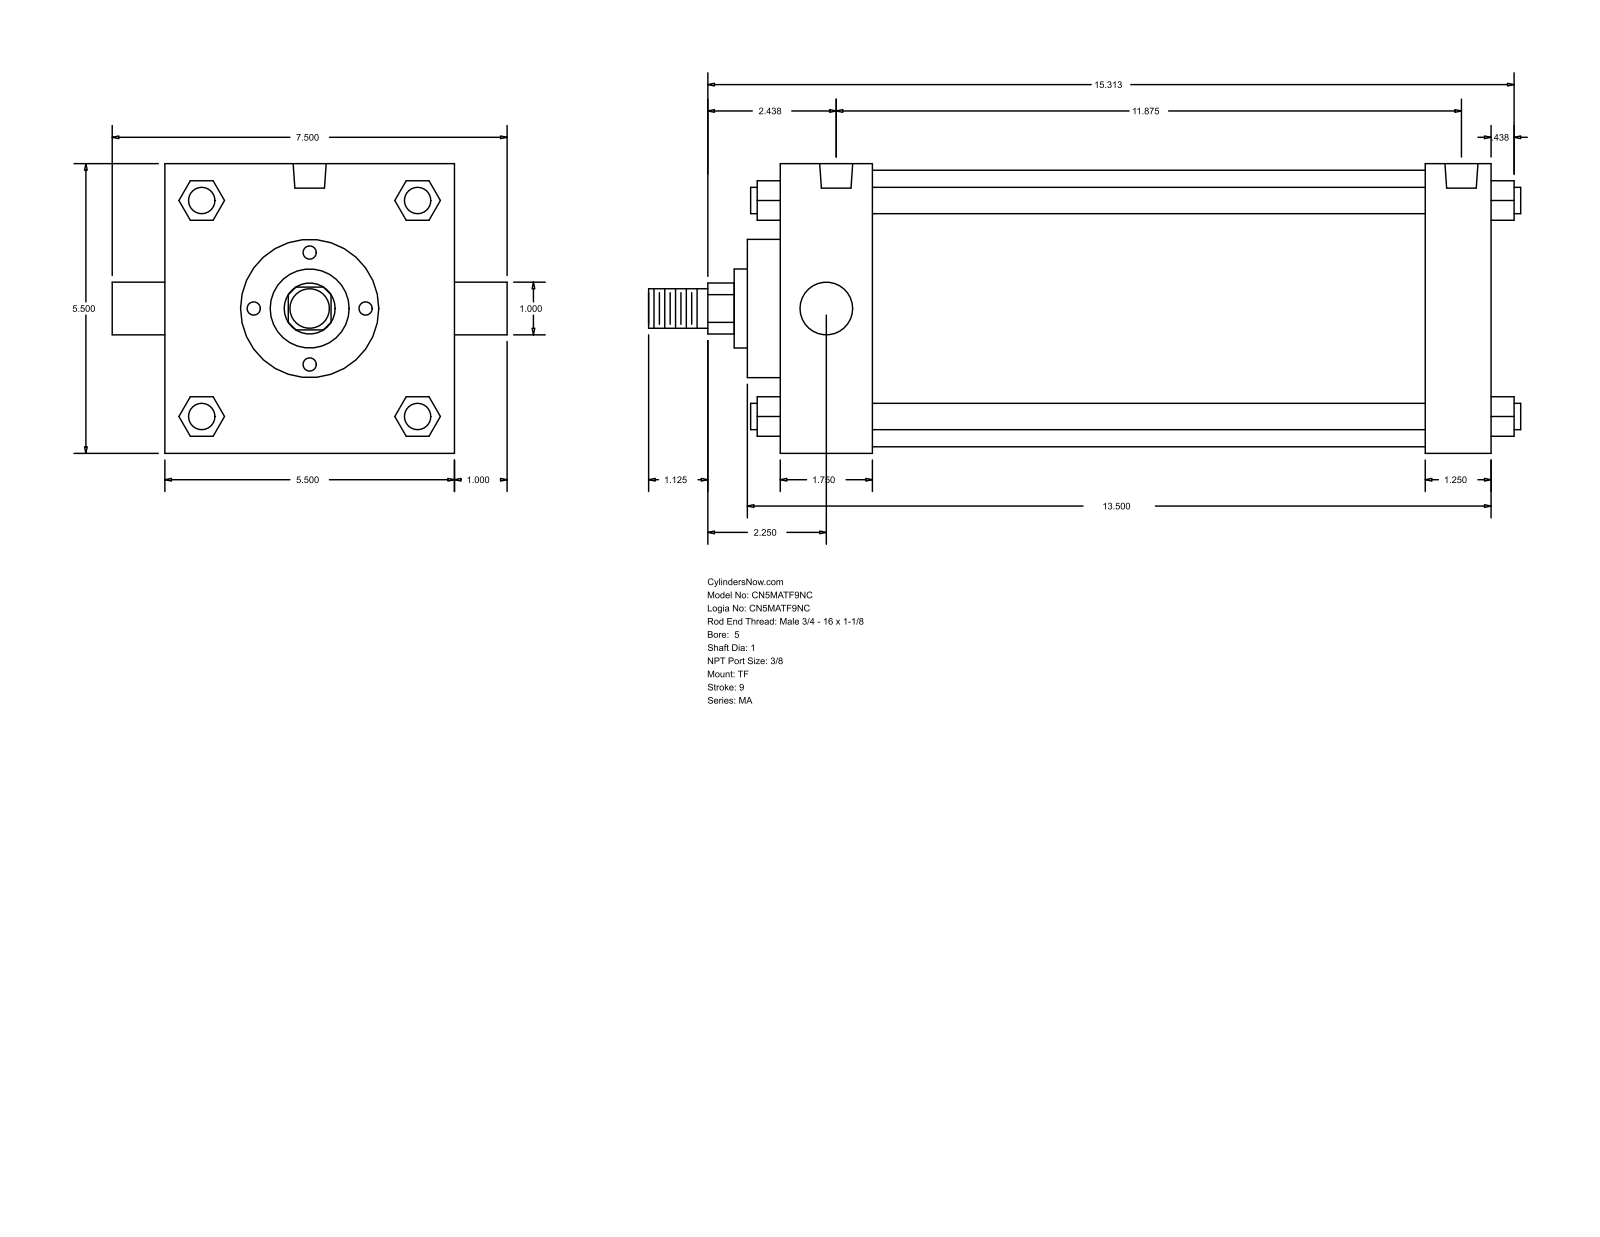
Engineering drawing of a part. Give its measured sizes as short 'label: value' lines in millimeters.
name: MA_TF__0500_1
written by: GSSL Pune (CONFIG_CONTROL_DESIGN)
unit: mm
bodies: 0 solids, 122 faces (93 planar, 29 cylindrical, 0 other)
size: 420.69 × 190.5 × 139.7
holes: 3× ⌀11.11, 2× ⌀15.93
bosses: 4× ⌀12.7, 2× ⌀25.4, 1× ⌀133.35, 1× ⌀66.67, 1× ⌀38.1, 1× ⌀19.05
rounds: 1× R12.29
face distances: 139.7, 342.9, 311.15, 31.75, 44.46, 266.69, 298.44, 15.87, 60.33, 327.02
hole spacings: 4.76, 4.77, 292.1, 296.86, 296.87, 301.63
